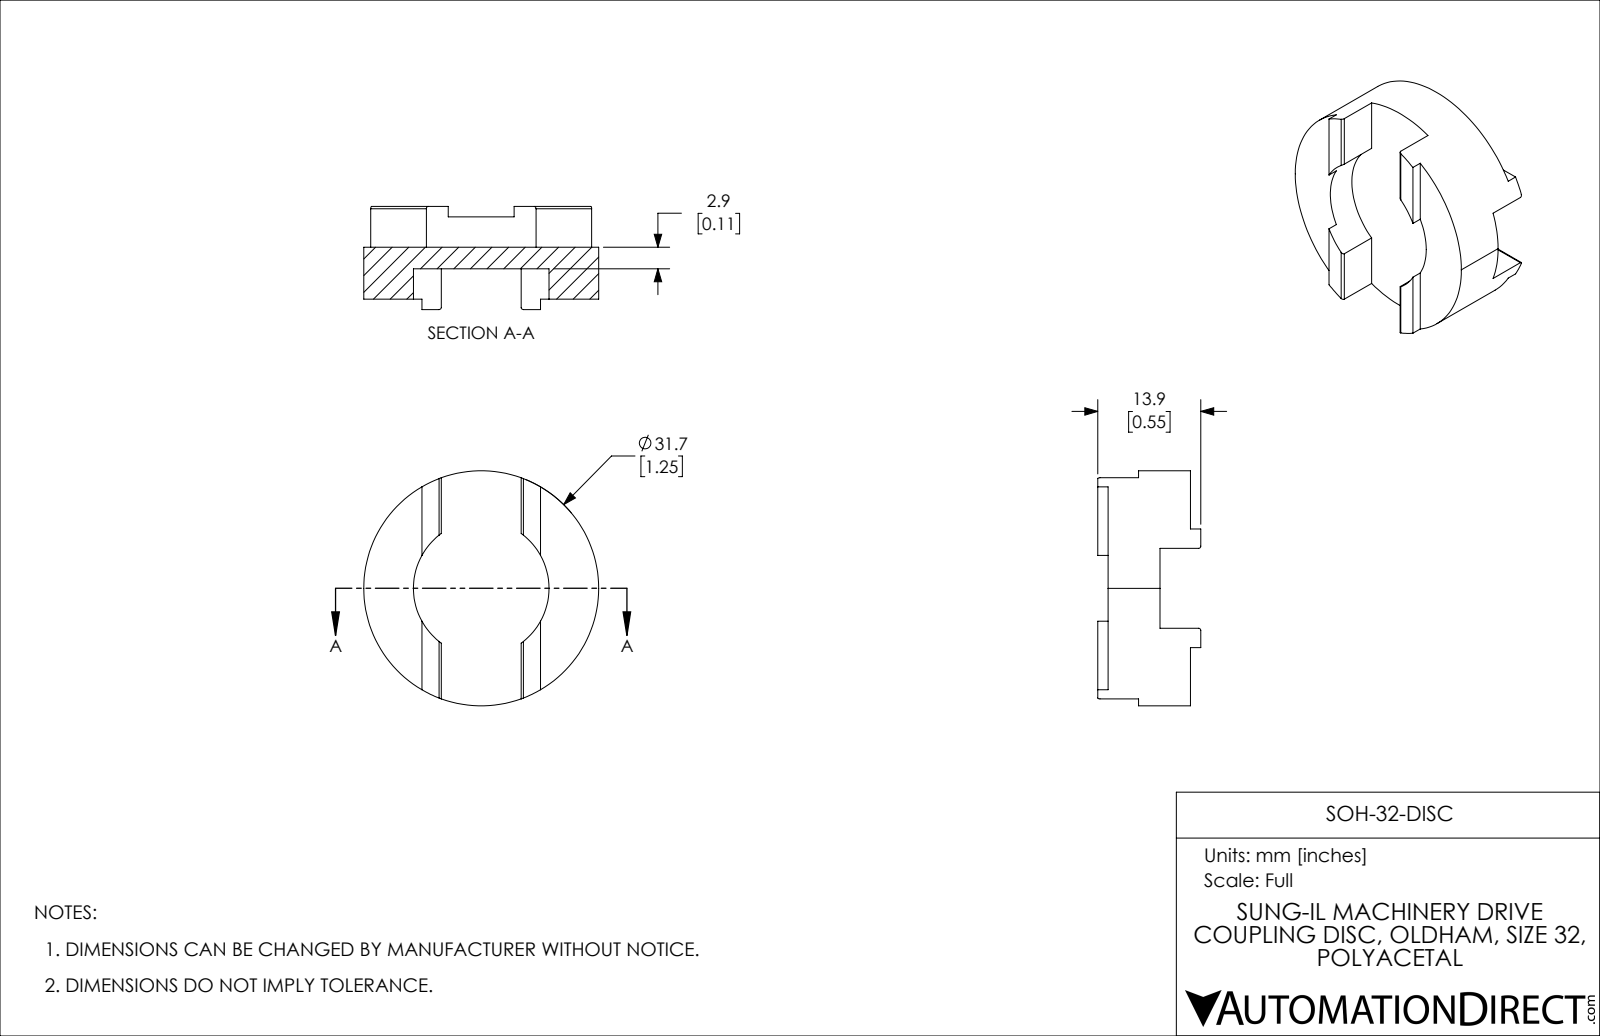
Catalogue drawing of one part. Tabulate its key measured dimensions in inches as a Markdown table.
| quantity | value |
| --- | --- |
| part name | SOH-32-DISC |
| STEP written by | SolidWorks 2021 (CONFIG_CONTROL_DESIGN) |
| units | inches |
| bodies | 1 solid, 45 faces (30 planar, 15 cylindrical, 0 other) |
| overall size | 1.248 × 1.248 × 0.547 |
| volume | 0.343 in³ |
| surface area | 5.098 in² |
| round holes (diameter × count) | 0.72 × 1 |
| round bosses / shafts (diameter × count) | 1.248 × 1 |
| partial cylindrical surfaces (radius × count) | 0.012 × 4 |
| main face-to-face distances | 0.161, 0.276, 0.114, 0.437, 0.424, 0.055, 0.217, 0.331, 0.492, 0.103 |
